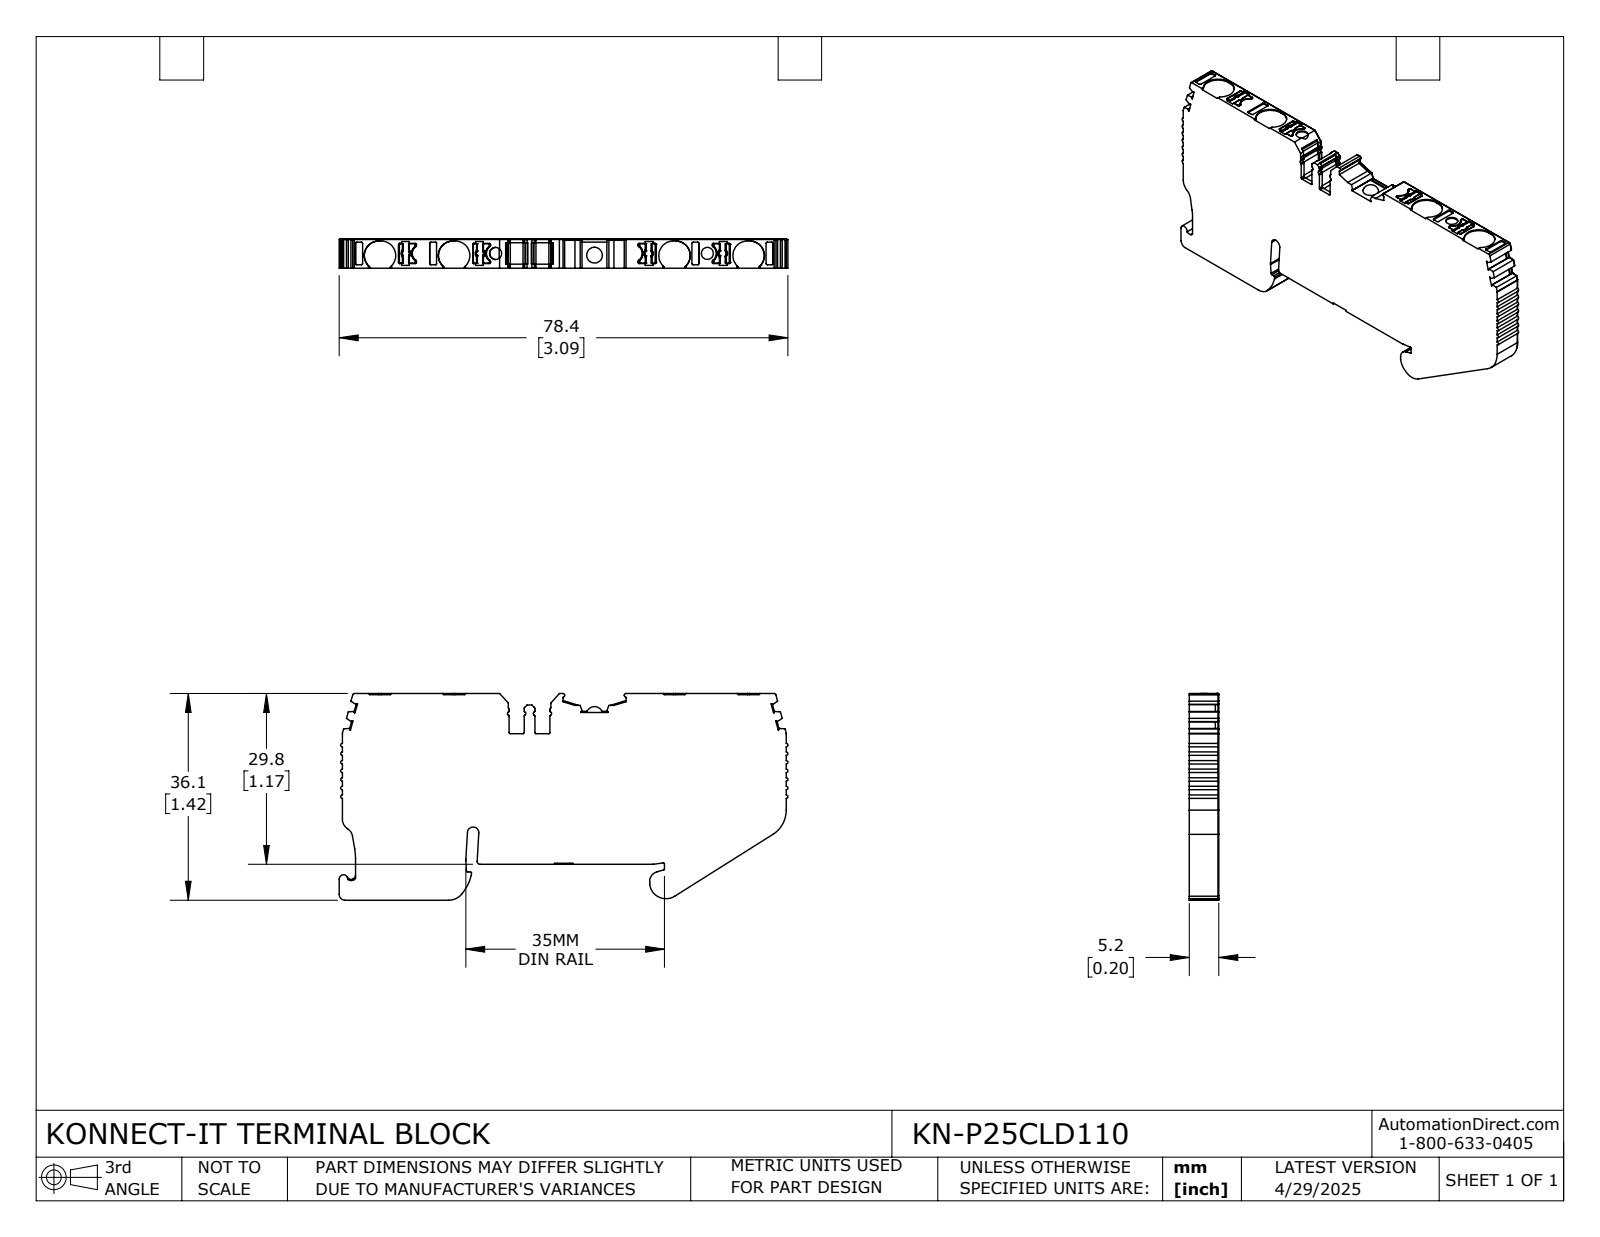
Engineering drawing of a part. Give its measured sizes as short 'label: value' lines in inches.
name: KN-P25CLD110
written by: SolidWorks 2024 (CONFIG_CONTROL_DESIGN)
unit: in
bodies: 1 solid, 744 faces (381 planar, 291 cylindrical, 72 other)
size: 3.085 × 1.42 × 0.203
volume: 0.731 in³; area: 9.642 in²
holes: 2× ⌀0.083
rounds: 78× R0.008, 39× R0.012, 21× R0.004, 18× R0.02, 16× R0.006, 9× R0.016, 8× R0.1, 4× R0.059
face distances: 0.203, 1.166, 1.174, 0.246, 1.412, 1.42, 3.052, 0.047, 0.197, 0.177
hole spacings: 1.456
